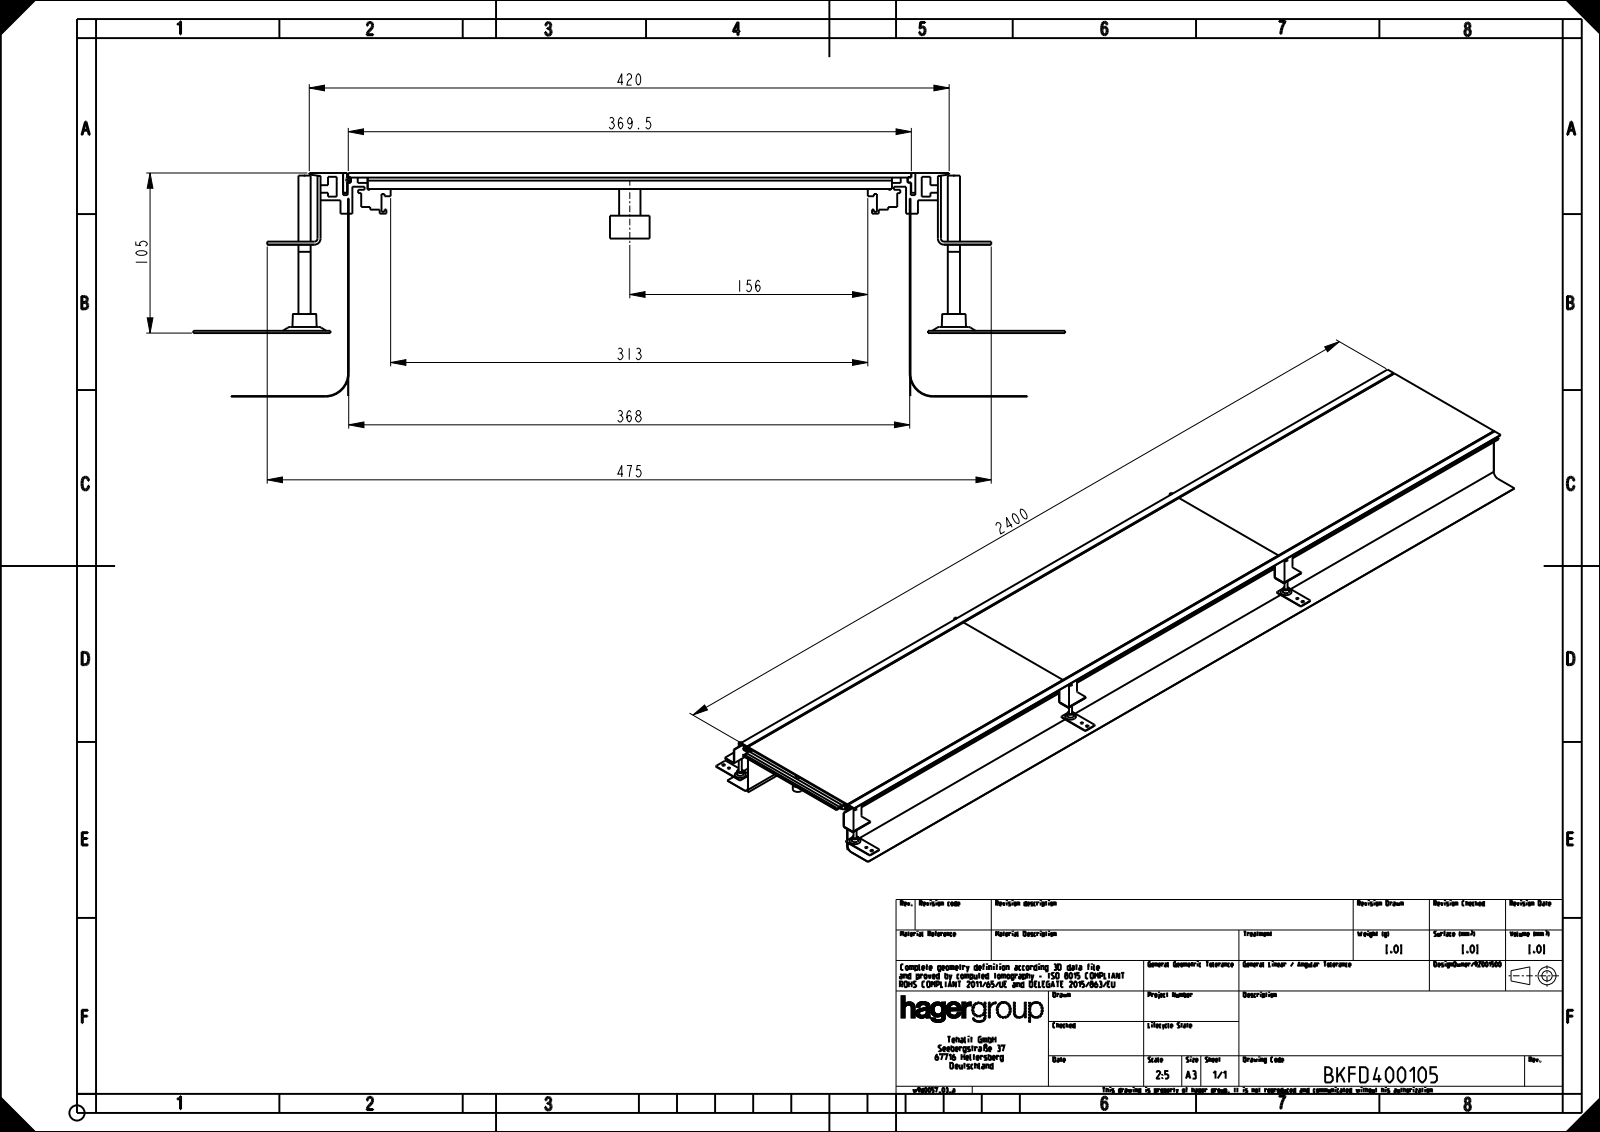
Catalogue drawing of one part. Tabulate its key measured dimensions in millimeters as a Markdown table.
| quantity | value |
| --- | --- |
| part name | U05644KUN; U05650KUN; U05994KUN; U05647KUN (+8 more) |
| STEP written by | CREO PARAMETRIC BY PTC INC, 2020281 (AUTOMOTIVE_DESIGN) |
| units | millimeters |
| bodies | 62 solids, 1026 faces (600 planar, 354 cylindrical, 72 other) |
| overall size | 2432.5 × 572.13 × 146.7 |
| volume | 7 081 000 mm³ |
| surface area | 5 962 000 mm² |
| round holes (diameter × count) | 7 × 15, 8 × 9, 10 × 9, 6 × 6, 8.5 × 6, 11.5 × 6, 17.5 × 6, 23 × 6 |
| round bosses / shafts (diameter × count) | 26 × 9, 14 × 9, 11.9 × 9, 20 × 6, 8 × 6 |
| partial cylindrical surfaces (radius × count) | 2 × 92, 3 × 24, 0.5 × 20, 4 × 2, 15 × 2, 15.4 × 2 |
| main face-to-face distances | 3, 0.4, 368.55, 143.7, 146.7, 143.3, 146.3, 368.95, 368.15, 6.5 |
| hole center spacings | 800, 1600, 800.25, 801.1, 802.4, 926.9, 937.16, 959.71 |
